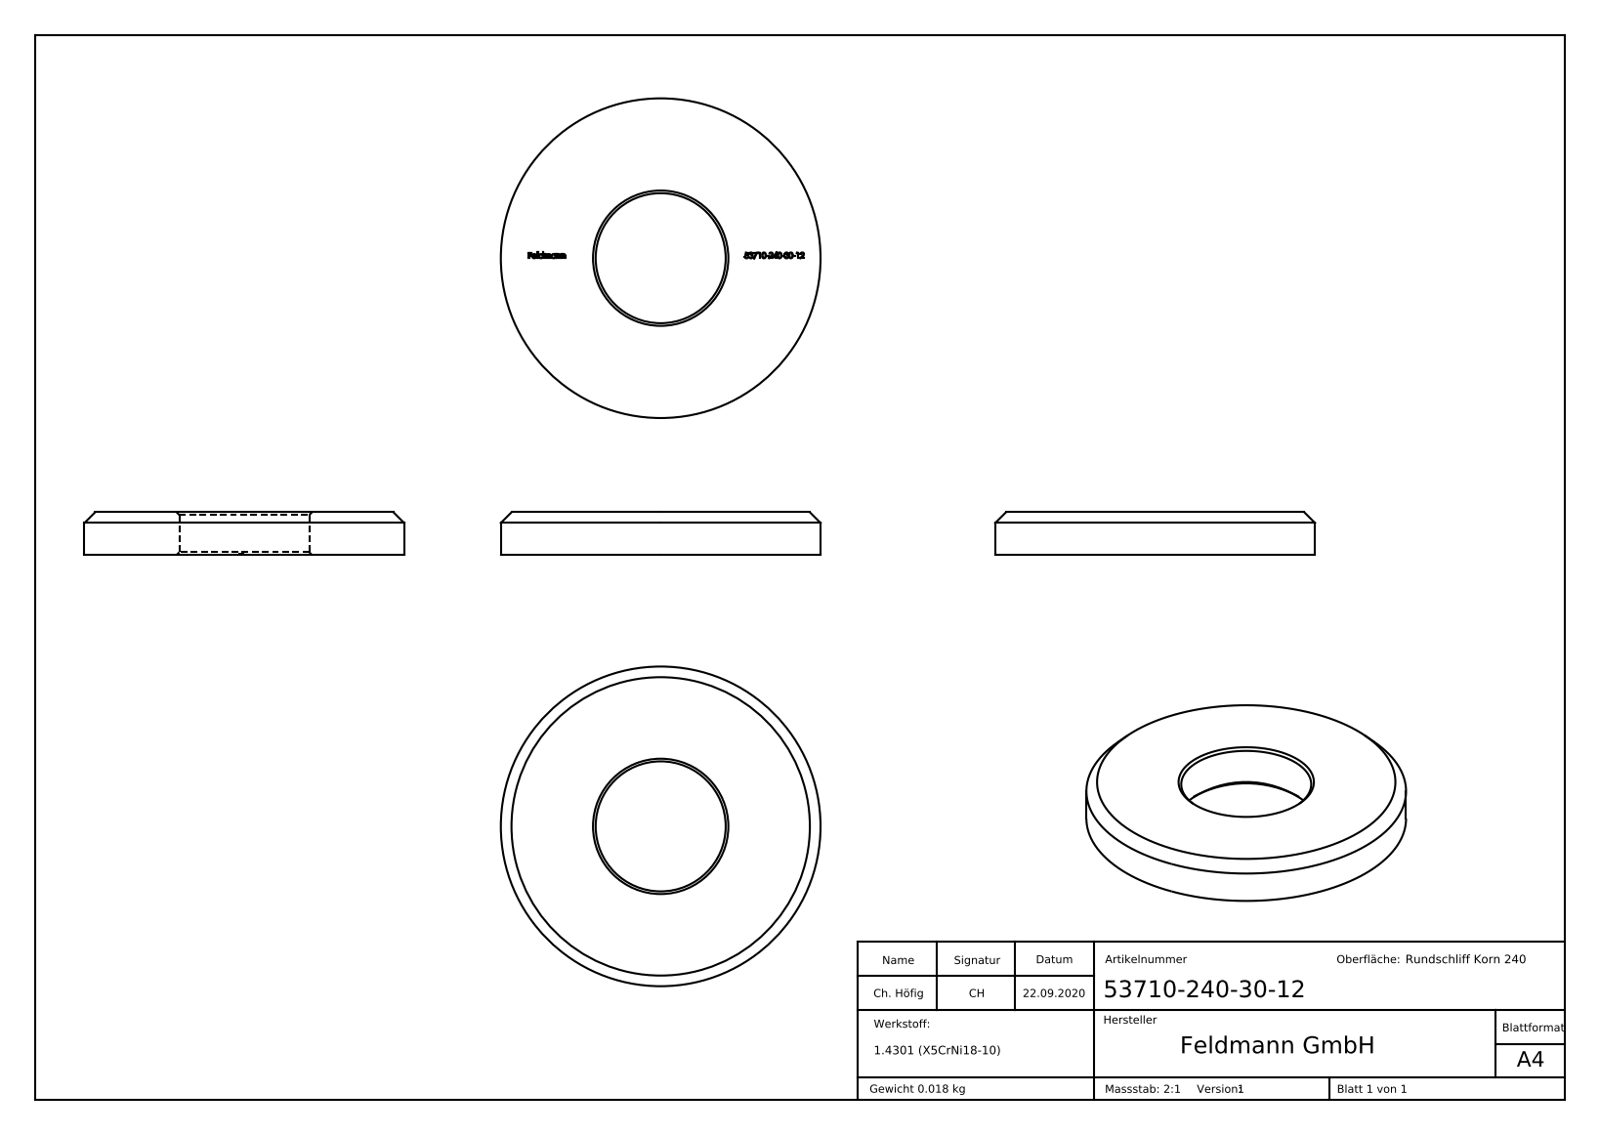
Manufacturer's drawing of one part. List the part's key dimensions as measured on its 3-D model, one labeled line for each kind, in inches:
Part name (STEP PRODUCT): 53710-240-30-12
STEP written by: SolidWorks 2018 (CONFIG_CONTROL_DESIGN)
Units: inches
Bodies: 1 solid, 286 faces (153 planar, 4 cylindrical, 129 other)
Overall size (bounding box): 1.181 × 1.181 × 0.157
Volume: 0.141 in³ · Surface area: 2.553 in²
Round holes (diameter × count): ⌀0.48 ×1
Round bosses / shafts (diameter × count): ⌀1.181 ×1
Main face-to-face distances: 0.157, 0.154, 0.014, 0.021, 0.022, 0.02, 0.821, 0.962, 0.141, 0.032
